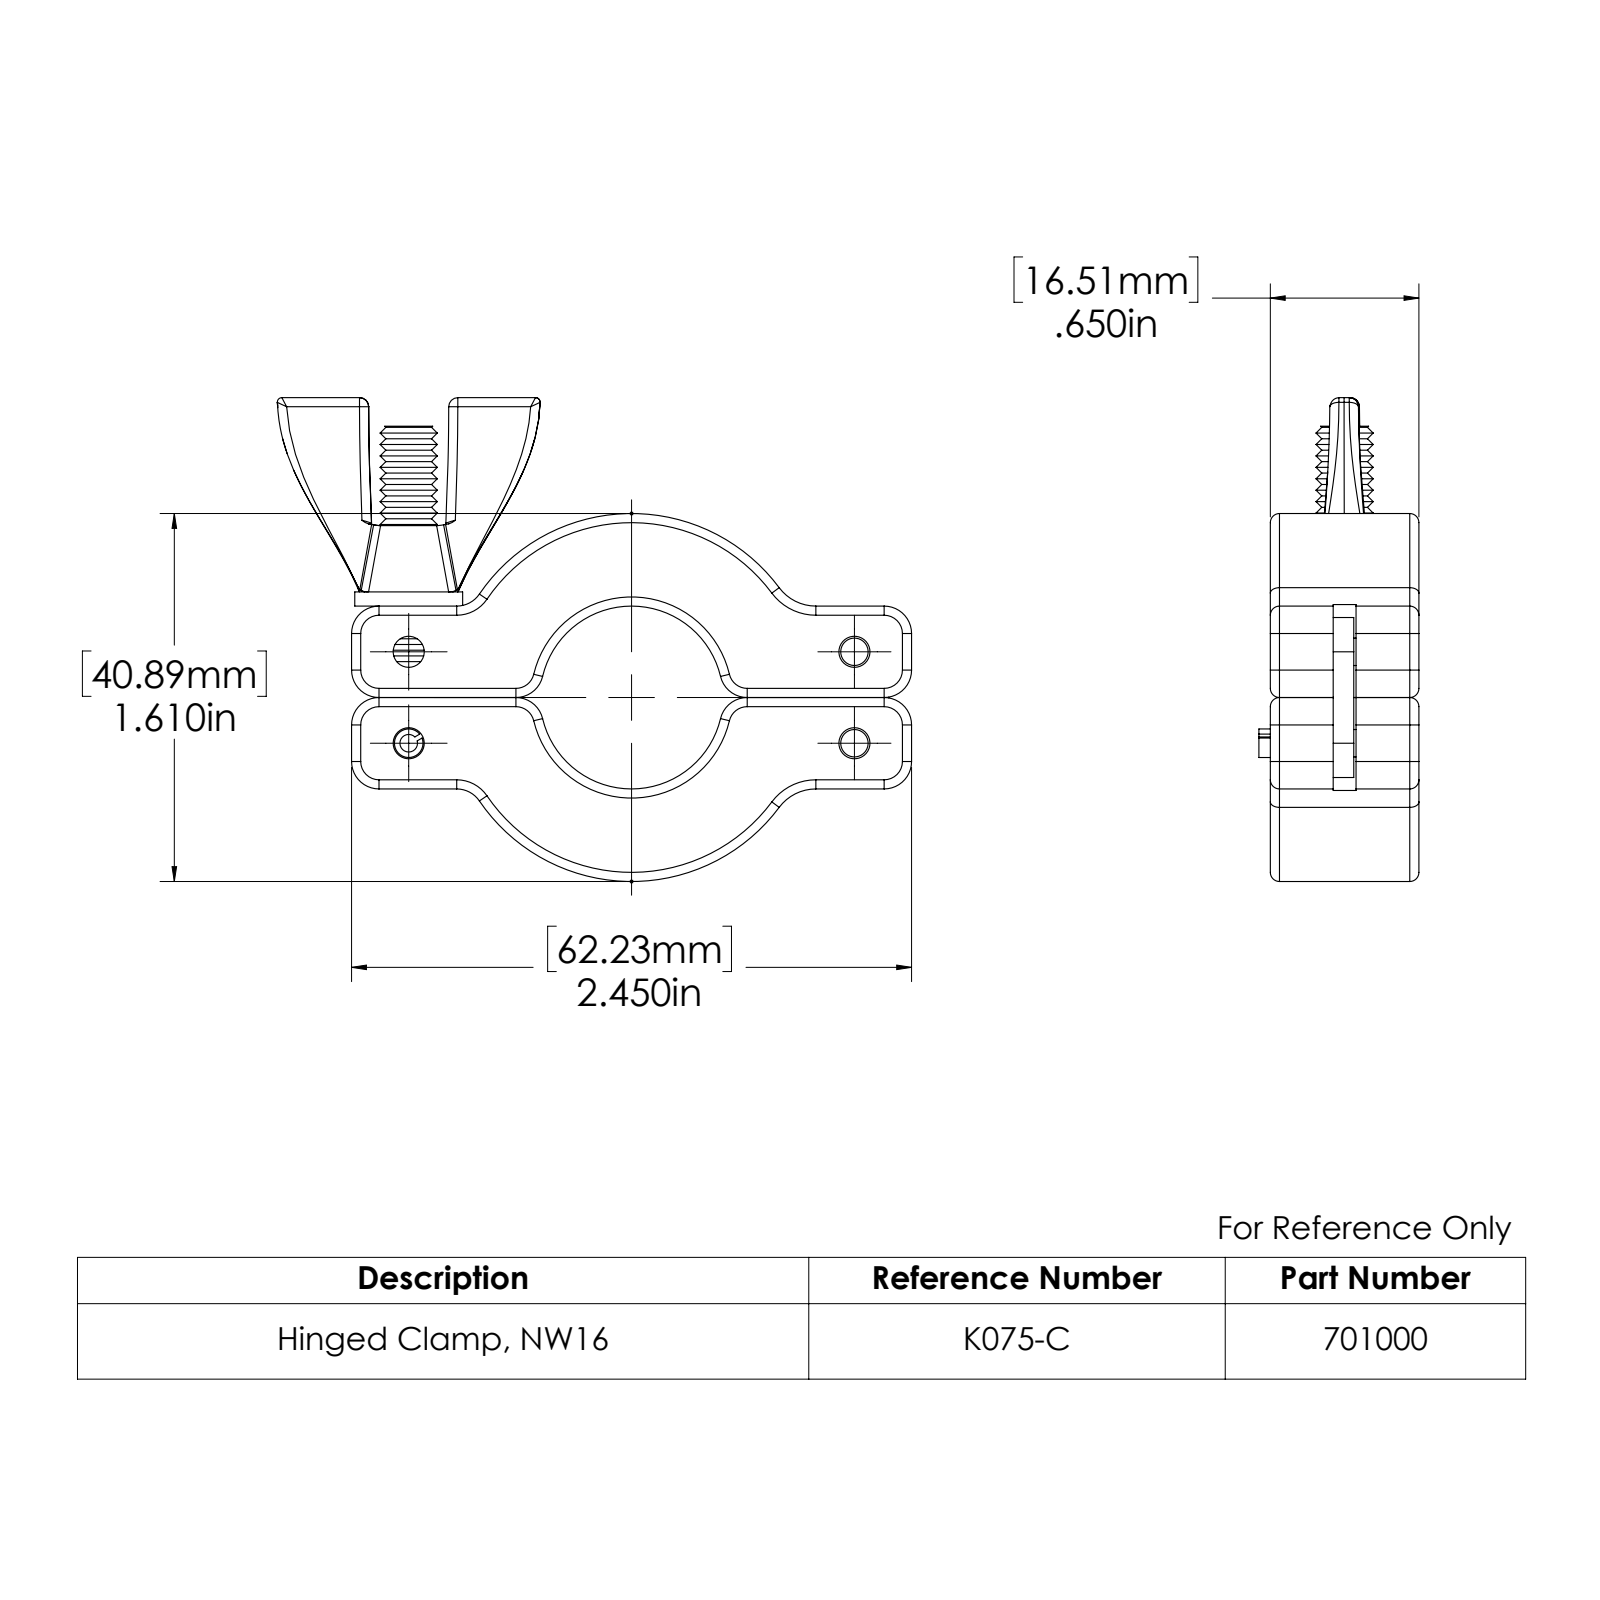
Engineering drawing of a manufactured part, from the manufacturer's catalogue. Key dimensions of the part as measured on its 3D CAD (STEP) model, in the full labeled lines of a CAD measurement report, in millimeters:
Part name (STEP PRODUCT): 701000; sub2; sub1
STEP written by: SolidWorks 2022 (AUTOMOTIVE_DESIGN)
Units: millimetres
Bodies: 9 solids, 381 faces (63 planar, 117 cylindrical, 201 other)
Overall size (bounding box): 70.5 × 53.8 × 17.8
Volume: 15 900 mm³ · Surface area: 13 770 mm²
Round holes (diameter × count): ⌀3.5 ×4, ⌀2 ×1, ⌀6.4 ×1, ⌀6.6 ×1, ⌀20.3 ×1, ⌀35.8 ×1
Round bosses / shafts (diameter × count): ⌀3 ×2, ⌀12 ×1, ⌀3.2 ×1
Partial cylindrical surfaces — rounded edges, fillets, slot ends (radius × count): R3 ×14, R1 ×12, R3.8 ×2, R5.1 ×2, R28.7 ×2, R3.3 ×1, R20.4 ×1
Main face-to-face distances: 16.5, 2.3, 11.9, 14.2, 14.2, 2.3, 7.2, 4.7, 10.2, 4.9
Hole centre spacings: 10.2, 25.3, 25.3, 49.5, 50.6
